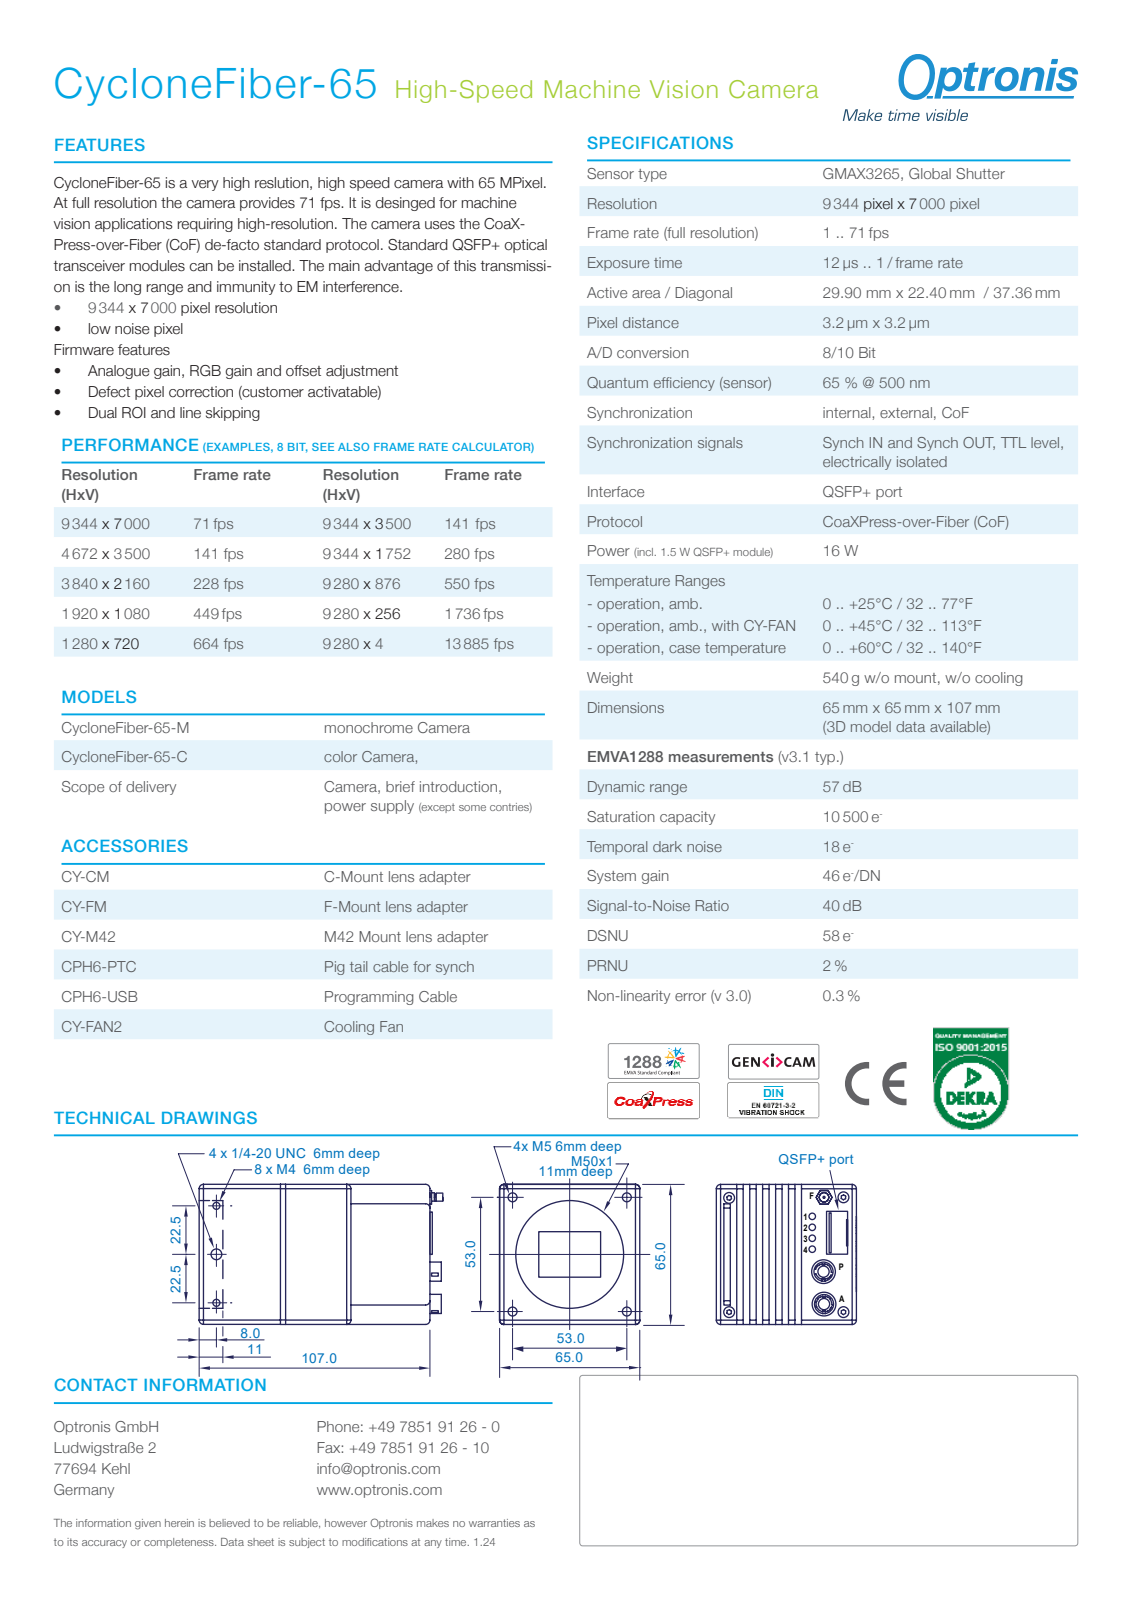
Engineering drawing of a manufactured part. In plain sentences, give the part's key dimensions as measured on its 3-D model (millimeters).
The part is named "1200-MG-54_CycloneFiber_long". Its 3-D file was written by "Autodesk Inventor 2026 (AUTOMOTIVE_DESIGN)". It is 5 solids with 5393 faces: 2714 planar, 2174 cylindrical and 505 other. Overall it measures 108.59 by 65 by 65 millimeters. Its volume is 137 431 cubic millimeters and its surface area 116 103 square millimeters. Round holes: 28 of diameter 1, 16 of diameter 0.8, 12 of diameter 2.7, 10 of diameter 0.5, 4 of diameter 1.57, 4 of diameter 2.01, 4 of diameter 2.2, 4 of diameter 2.85, 4 of diameter 3.24, 4 of diameter 4.2, 4 of diameter 5, 4 of diameter 5.5. Round bosses or shafts: 239 of diameter 0.97, 239 of diameter 0.3, 12 of diameter 1.1, 8 of diameter 3.8, 8 of diameter 2.5, 4 of diameter 4.7, 4 of diameter 4.5, 4 of diameter 2.8. Partial cylindrical surfaces (rounded edges, fillets, slot ends): 186 of radius 0.25, 60 of radius 0.2, 45 of radius 0.1, 40 of radius 0.5, 36 of radius 1, 34 of radius 2, 32 of radius 3, 28 of radius 0.13. The main face-to-face distances are 3, 6, 9, 12, 15, 18, 21, 24, 2, 27. The hole center spacings are 3.36, 7.83, 6.73, 12.7, 5, 10.97, 1.8, 7.2.
